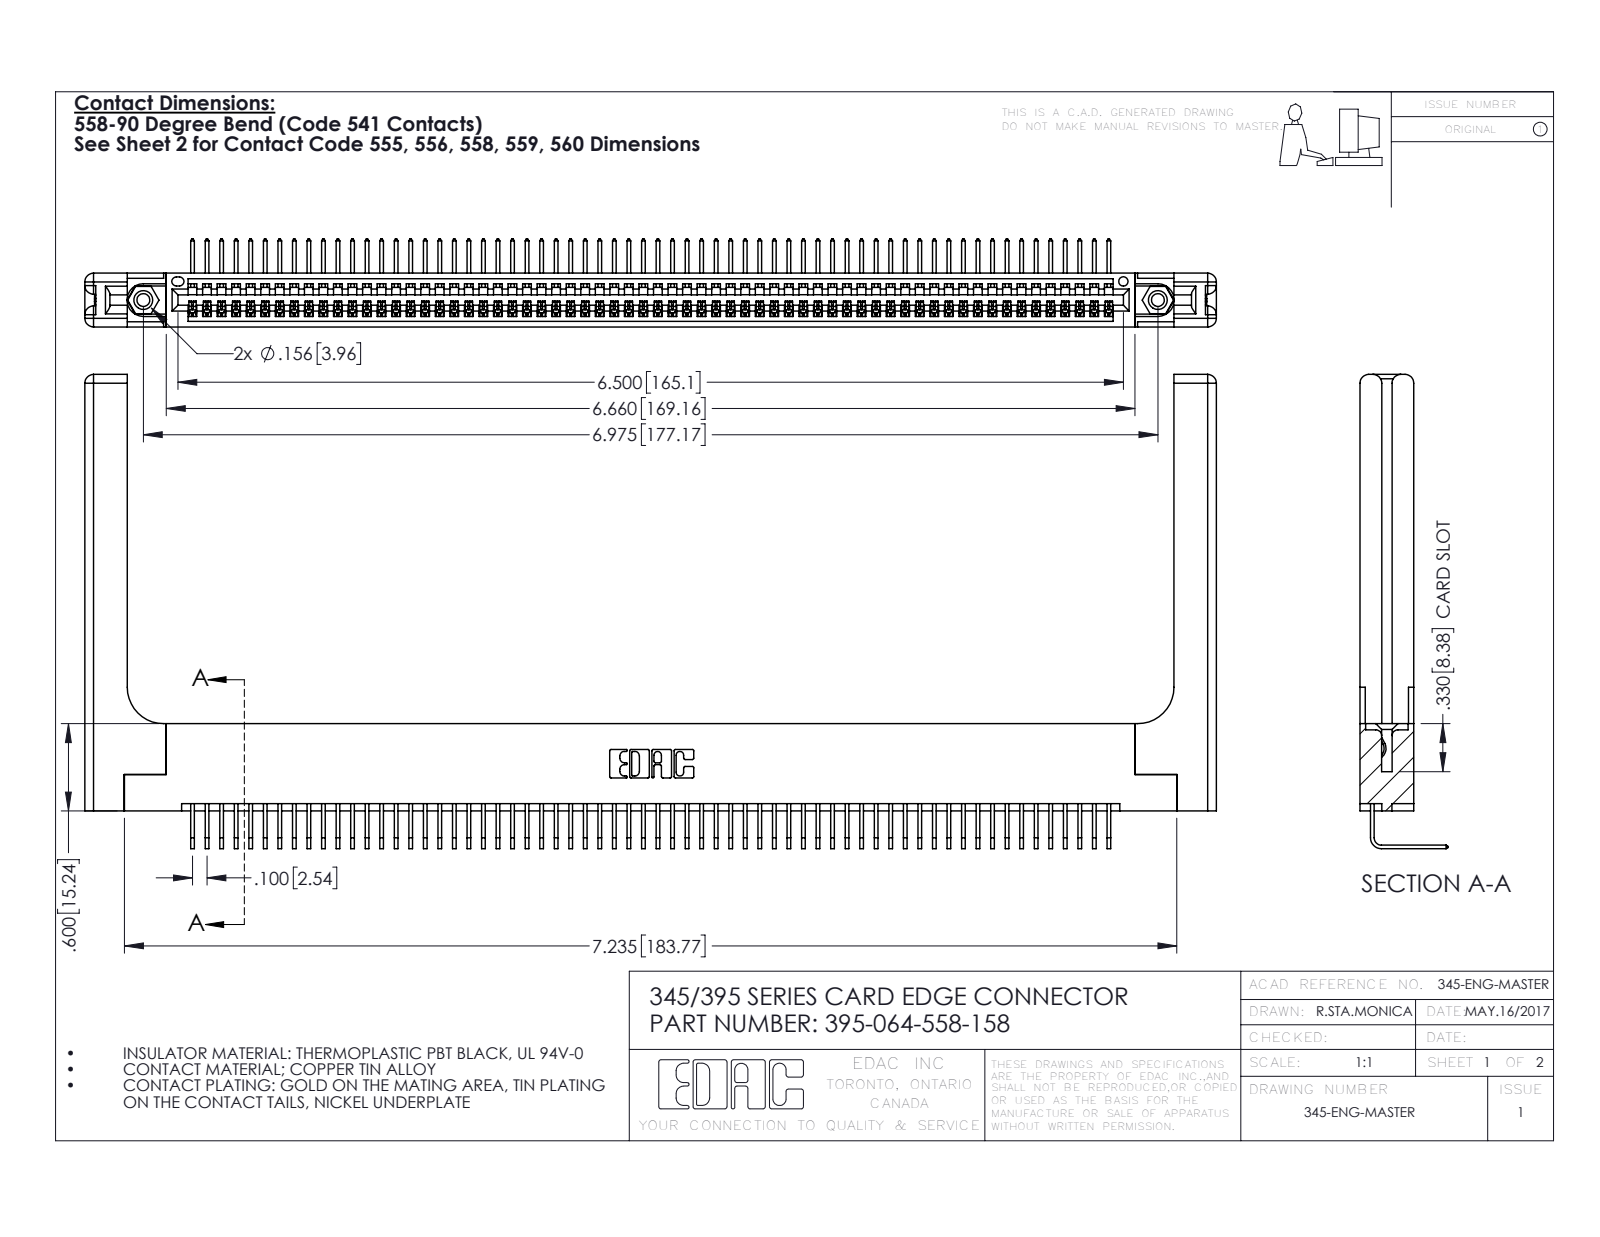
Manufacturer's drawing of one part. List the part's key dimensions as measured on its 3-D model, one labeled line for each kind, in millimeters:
Part name (STEP PRODUCT): 345 Part_Flush Mounting Lugs - 0.156 Dia-TH; 345-250-001_345-250-001-102; 395-064-558-158; 345-220-058_345-220-058 (+1 more)
STEP written by: SolidWorks 2016 (CONFIG_CONTROL_DESIGN)
Units: millimetres
Bodies: 69 solids, 4222 faces (2916 planar, 1246 cylindrical, 60 other)
Overall size (bounding box): 197.6 × 82.8 × 15.4
Volume: 27 660 mm³ · Surface area: 32 320 mm²
Round holes (diameter × count): ⌀2.3 ×2, ⌀3.2 ×2, ⌀4 ×2, ⌀1.6 ×1
Round bosses / shafts (diameter × count): ⌀3.9 ×2
Partial cylindrical surfaces — rounded edges, fillets, slot ends (radius × count): R0.2 ×128, R0.3 ×22, R1.5 ×16, R0.2 ×6, R0.8 ×6, R0.7 ×3, R0.8 ×2, R0.8 ×2
Main face-to-face distances: 1.8, 9.4, 7.6, 5.1, 2.5, 6.9, 0.6, 5.7, 3.8, 3.8
Hole centre spacings: 6.9, 171.2, 177.2
